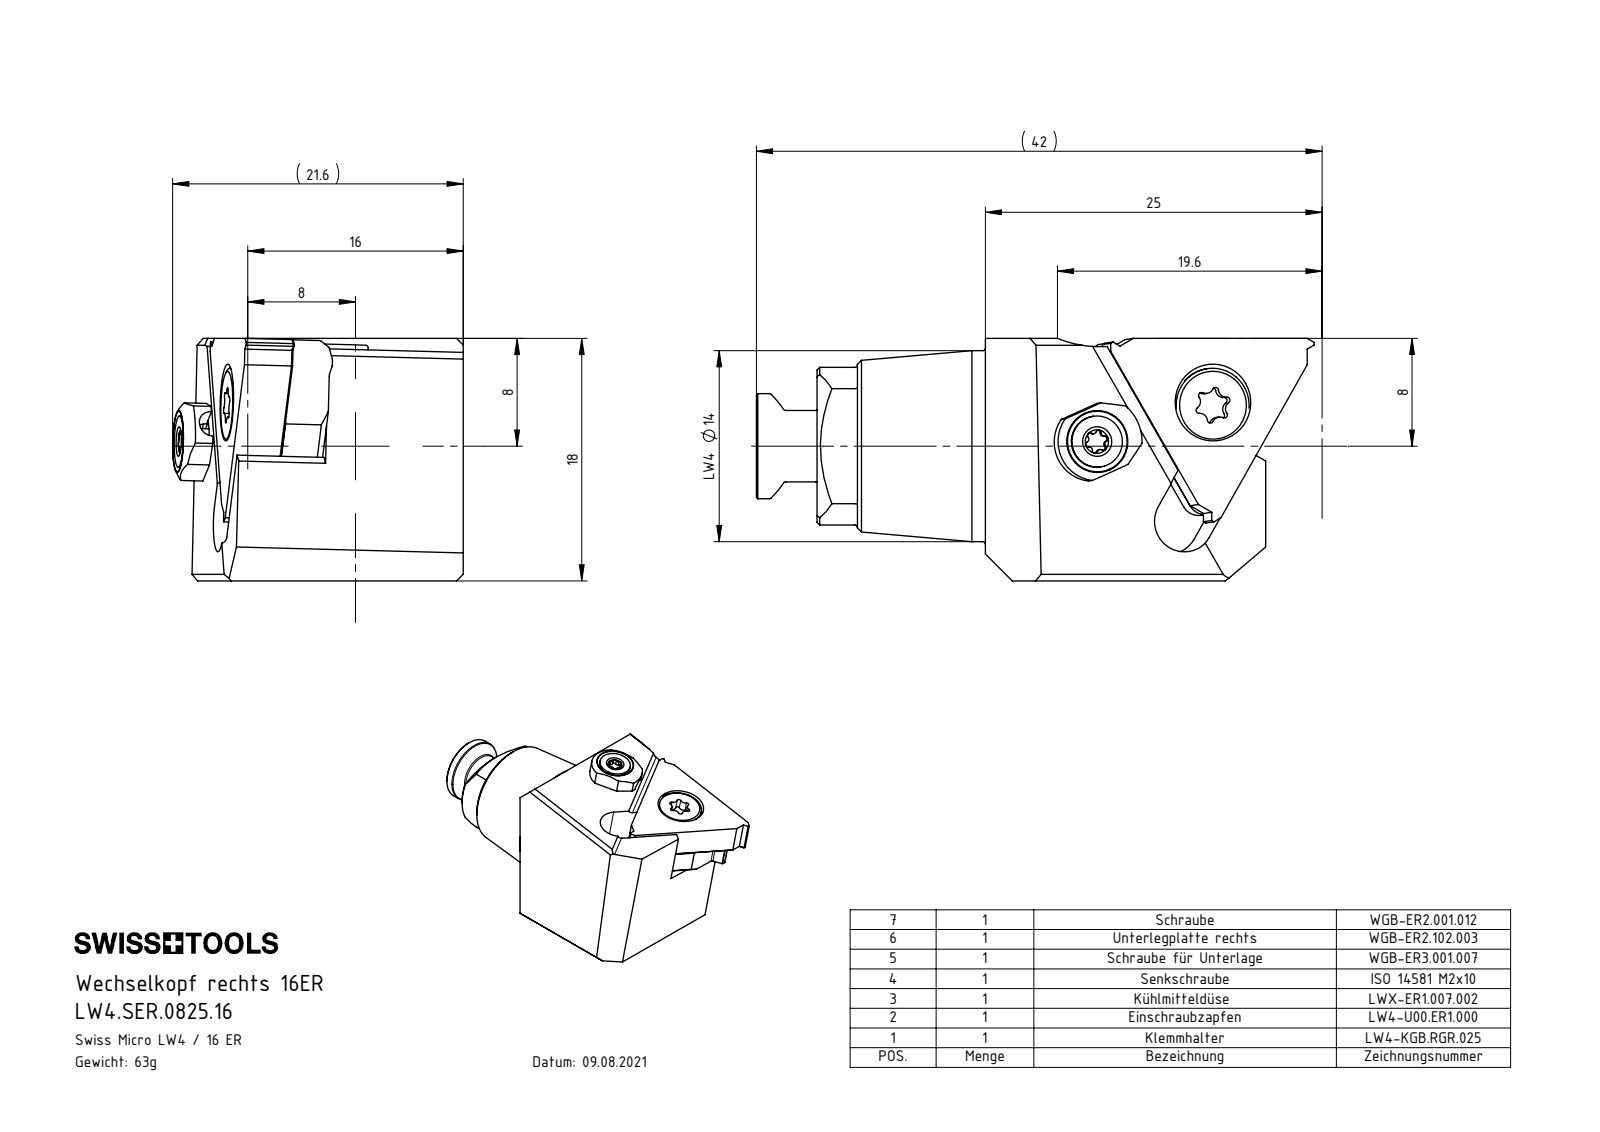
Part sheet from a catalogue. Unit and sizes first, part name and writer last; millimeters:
Units: millimetres
Overall size (bounding box): 41.41 × 21.58 × 18
Round holes (diameter × count): ⌀2.58 ×2, ⌀3 ×2, ⌀1.6 ×1, ⌀2 ×1, ⌀2.5 ×1, ⌀4 ×1, ⌀4.02 ×1, ⌀5.5 ×1
Round bosses / shafts (diameter × count): ⌀5.5 ×2, ⌀14.17 ×1, ⌀7.7 ×1, ⌀6 ×1, ⌀5.3 ×1, ⌀5 ×1, ⌀3.8 ×1, ⌀3.18 ×1
Partial cylindrical surfaces — rounded edges, fillets, slot ends (radius × count): R0.2 ×8, R0.23 ×6, R0.24 ×6, R0.34 ×6, R0.57 ×6, R0.57 ×6, R0.1 ×2, R2.9 ×2
Main face-to-face distances: 3.2, 3.65, 6.86, 3.21, 6.85, 3.66, 3.19, 18, 0.59, 7.5
Hole centre spacings: 9.5, 9.53, 9.56, 9.59, 474.14, 474.18, 479.53, 479.59
Volume: 7 629 mm³ · Surface area: 4 674 mm²
Bodies: 8 solids, 237 faces (106 planar, 76 cylindrical, 55 other)
Part name (STEP PRODUCT): WGB-ER2.102.003_A; LW4-KGB.RGR.025_A; LWX-ER1.007.002; WGB-ER2.001.012_A (+5 more)
STEP written by: SolidWorks 2017 (AUTOMOTIVE_DESIGN)
